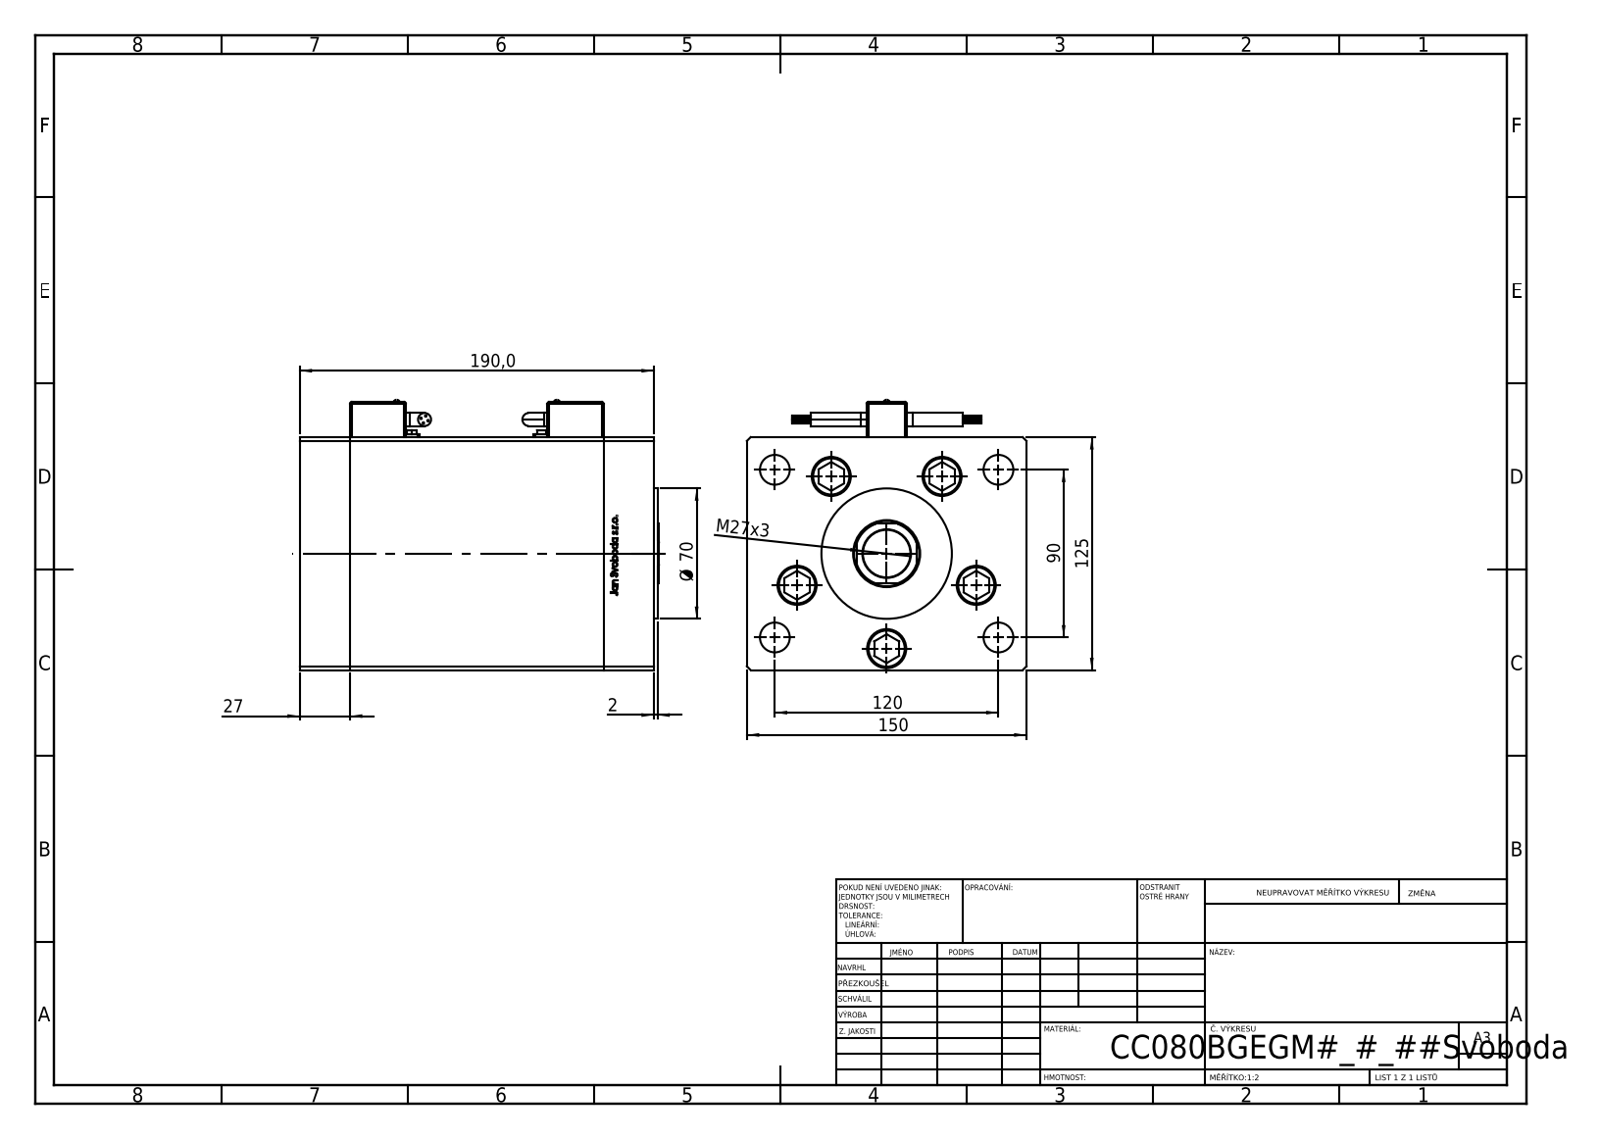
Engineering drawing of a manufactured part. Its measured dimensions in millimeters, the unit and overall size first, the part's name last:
Units: millimetres
Overall size (bounding box): 192.8 × 150 × 145.1
Round holes (diameter × count): ⌀17.5 ×5, ⌀21 ×5, ⌀16 ×4, ⌀2 ×2, ⌀3.6 ×2, ⌀5 ×2, ⌀7 ×2, ⌀13.16 ×2, ⌀25.5 ×1, ⌀36 ×1
Round bosses / shafts (diameter × count): ⌀0.85 ×8, ⌀8 ×5, ⌀7 ×4, ⌀6 ×2, ⌀3.5 ×2, ⌀2.5 ×2, ⌀80 ×1, ⌀70 ×1
Partial cylindrical surfaces — rounded edges, fillets, slot ends (radius × count): R1 ×24, R4 ×4, R0.93 ×2, R17.5 ×1
Main face-to-face distances: 27, 163, 125, 136, 150, 190, 7.8, 34.8, 128.2, 155.2
Hole centre spacings: 51, 75, 8.25, 30.43, 30.48, 53.93, 56.92, 58.89
Volume: 3 110 000 mm³ · Surface area: 345 293 mm²
Bodies: 16 solids, 1389 faces (542 planar, 237 cylindrical, 610 other)
Part name (STEP PRODUCT): V220C BACK_B; ALLEN BOLT; Magnetic_Switch_MSU4; V220C_FRONT_B (+2 more)
STEP written by: SolidWorks 2019 (CONFIG_CONTROL_DESIGN)
